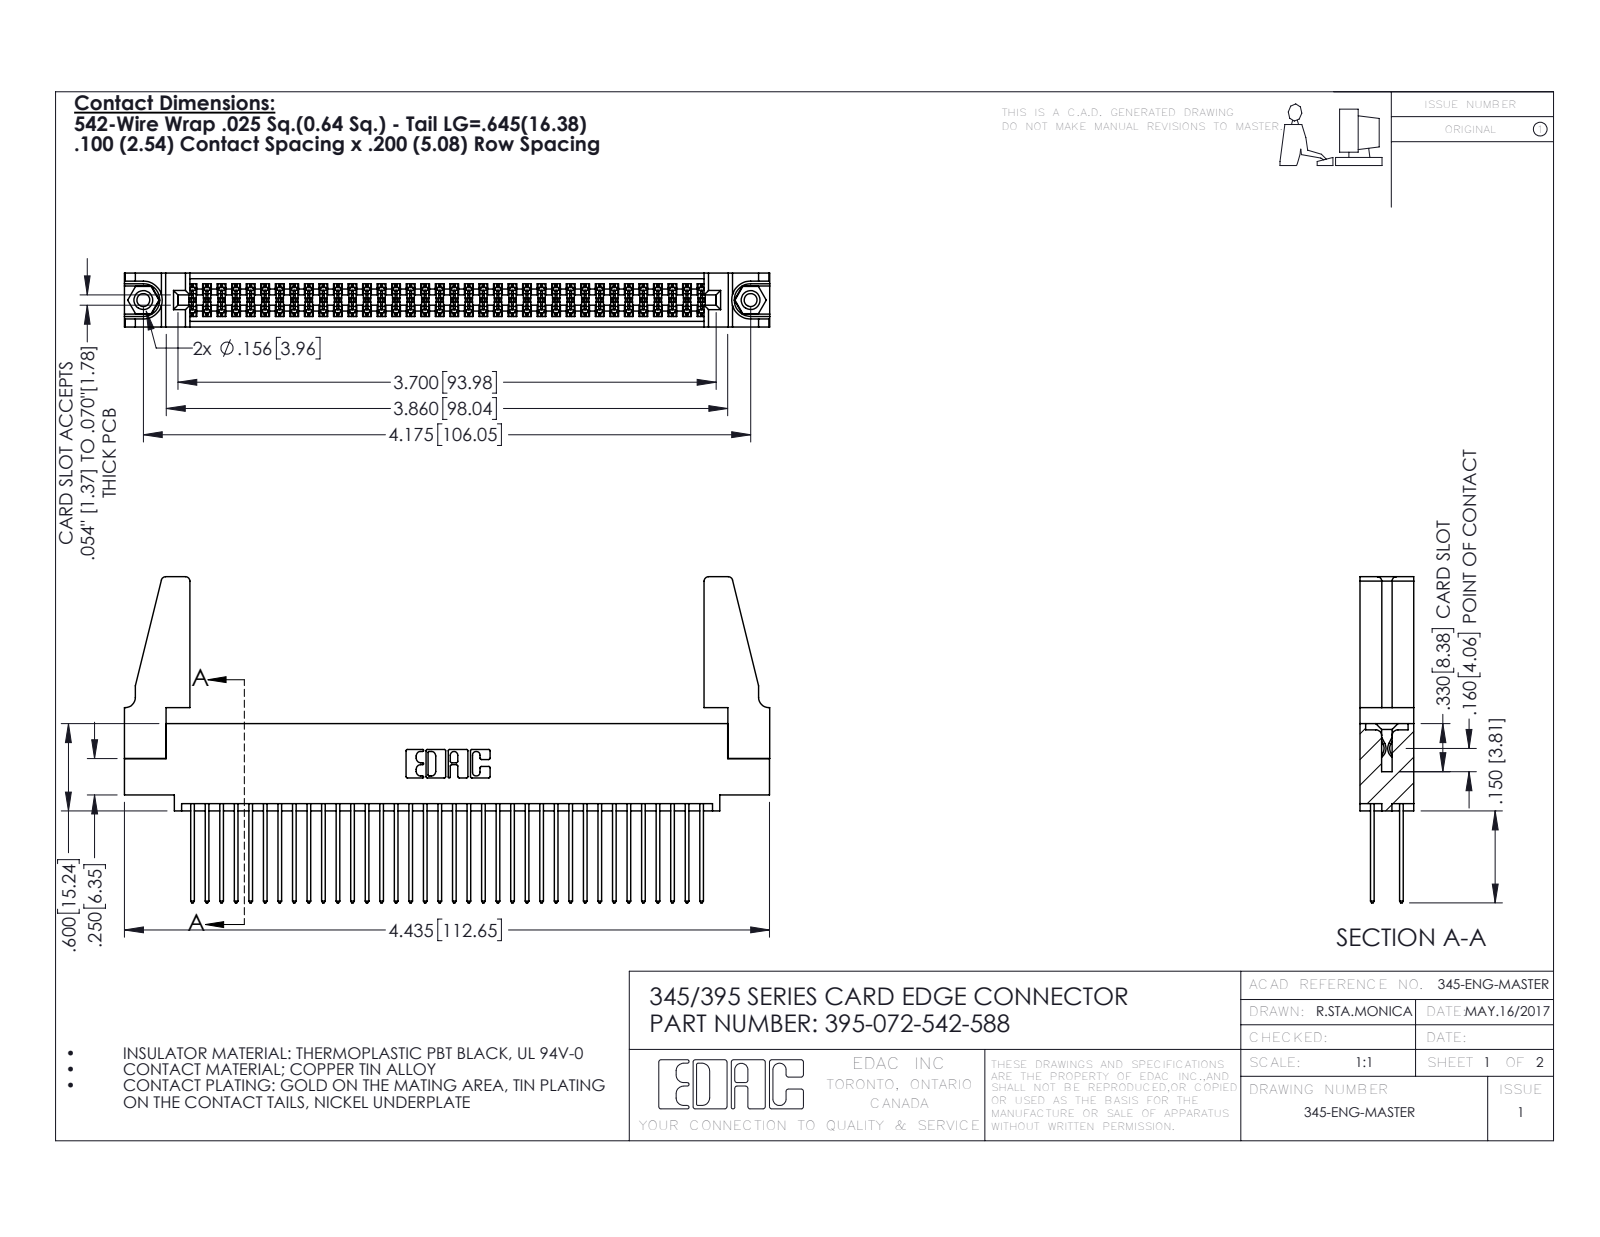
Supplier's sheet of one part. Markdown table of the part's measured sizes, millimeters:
| quantity | value |
| --- | --- |
| part name | 345 Part_0.110 Offset - 0.156 Dia-TH; 345-220-078_345-220-088; 345-292-001_345-293-142; 395-072-542-588 (+1 more) |
| STEP written by | SolidWorks 2016 (CONFIG_CONTROL_DESIGN) |
| units | millimeters |
| bodies | 77 solids, 3854 faces (2532 planar, 1306 cylindrical, 16 other) |
| overall size | 112.7 × 56.9 × 9.4 |
| volume | 14 400 mm³ |
| surface area | 21 150 mm² |
| round holes (diameter × count) | 2.3 × 2, 3.2 × 2, 4 × 2, 1.6 × 1 |
| round bosses / shafts (diameter × count) | 3.9 × 2 |
| partial cylindrical surfaces (radius × count) | 0.2 × 108, 0.3 × 72, 0.3 × 22, 0.8 × 8, 0.2 × 6, 0.8 × 6, 0.7 × 3, 0.4 × 2 |
| main face-to-face distances | 1.8, 7.6, 5.1, 2.5, 6.9, 0.6, 9.4, 5.7, 4.4, 3.8 |
| hole center spacings | 6.9, 100.1, 106 |
